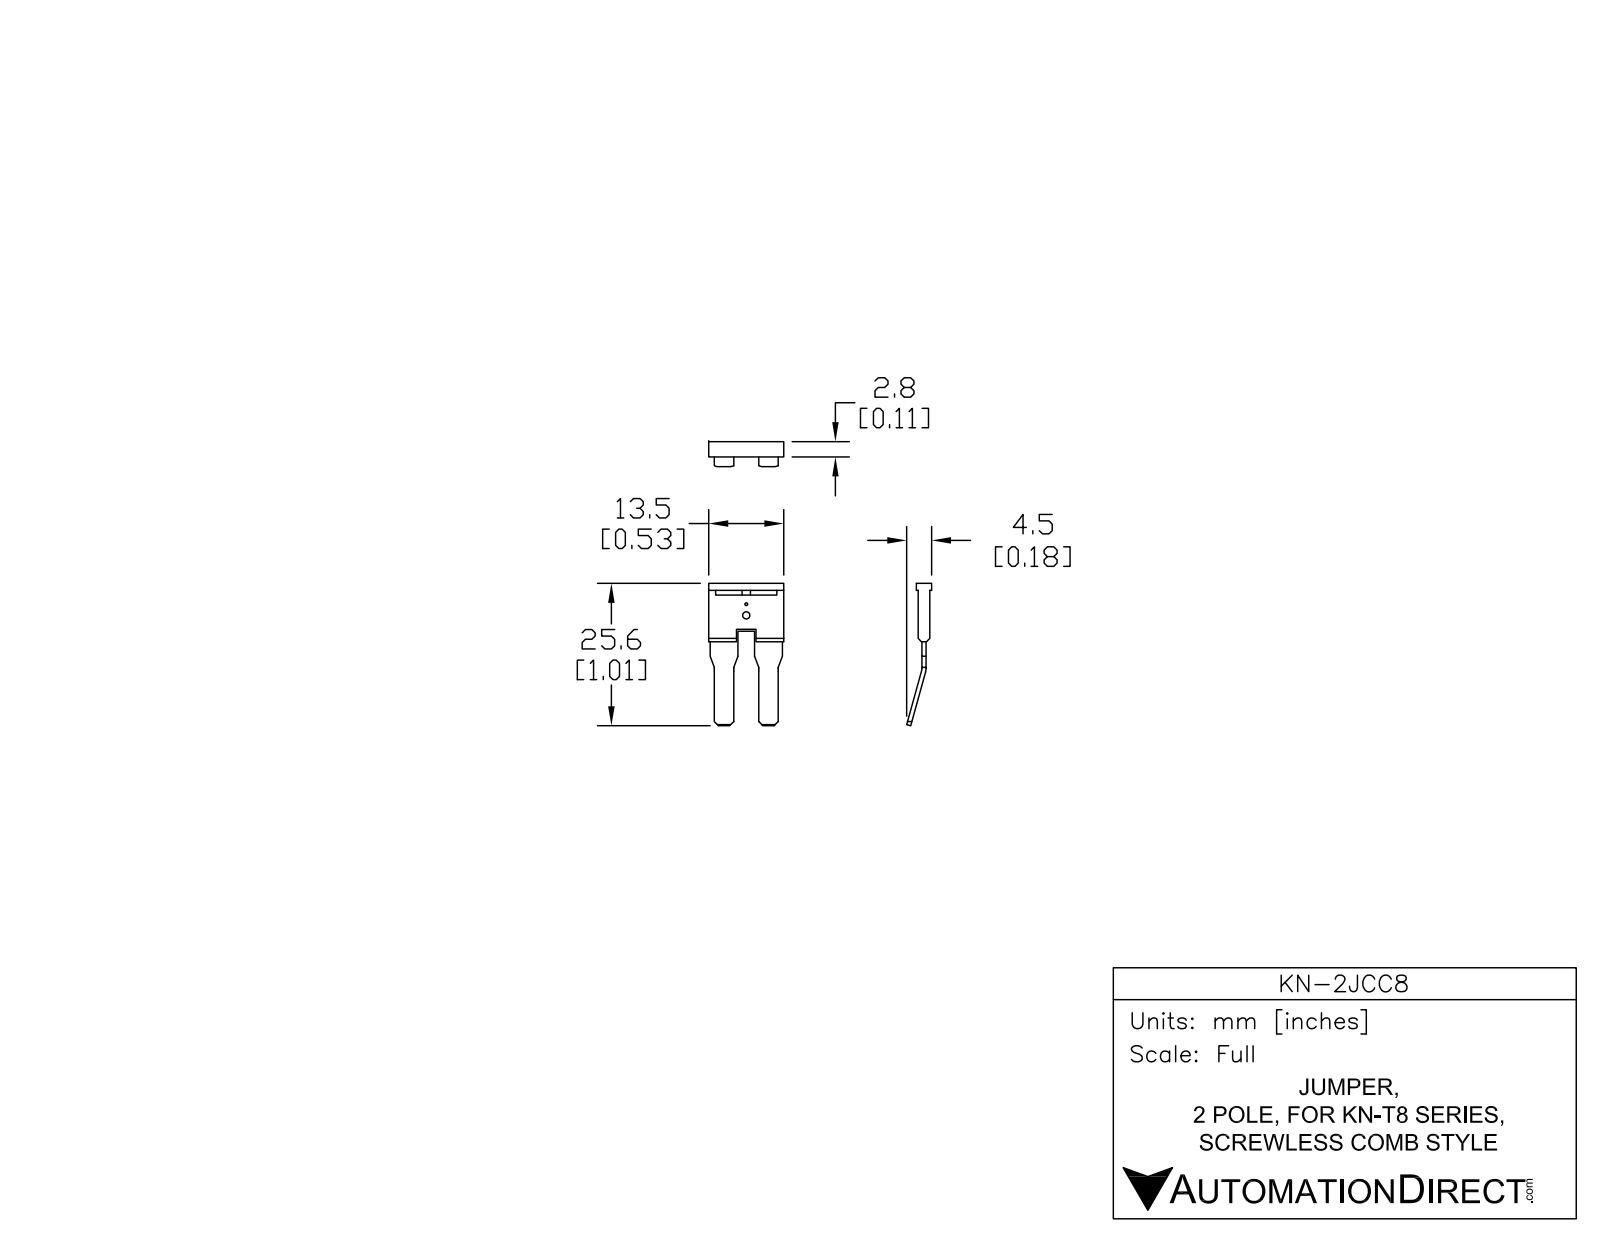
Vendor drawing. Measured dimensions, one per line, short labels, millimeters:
name: KN-2JCC8
written by: SolidWorks 2014 (AUTOMOTIVE_DESIGN)
unit: mm
bodies: 1 solid, 68 faces (56 planar, 12 cylindrical, 0 other)
size: 25.6 × 13.5 × 4.49
volume: 358 mm³; area: 709 mm²
holes: 1× ⌀0.5, 1× ⌀1.3
rounds: 1× R1.62, 1× R2.38
face distances: 0.75, 2.1, 1, 0.67, 1.43, 1.42, 0.68, 1.25, 1.75, 4.5
hole spacings: 2
